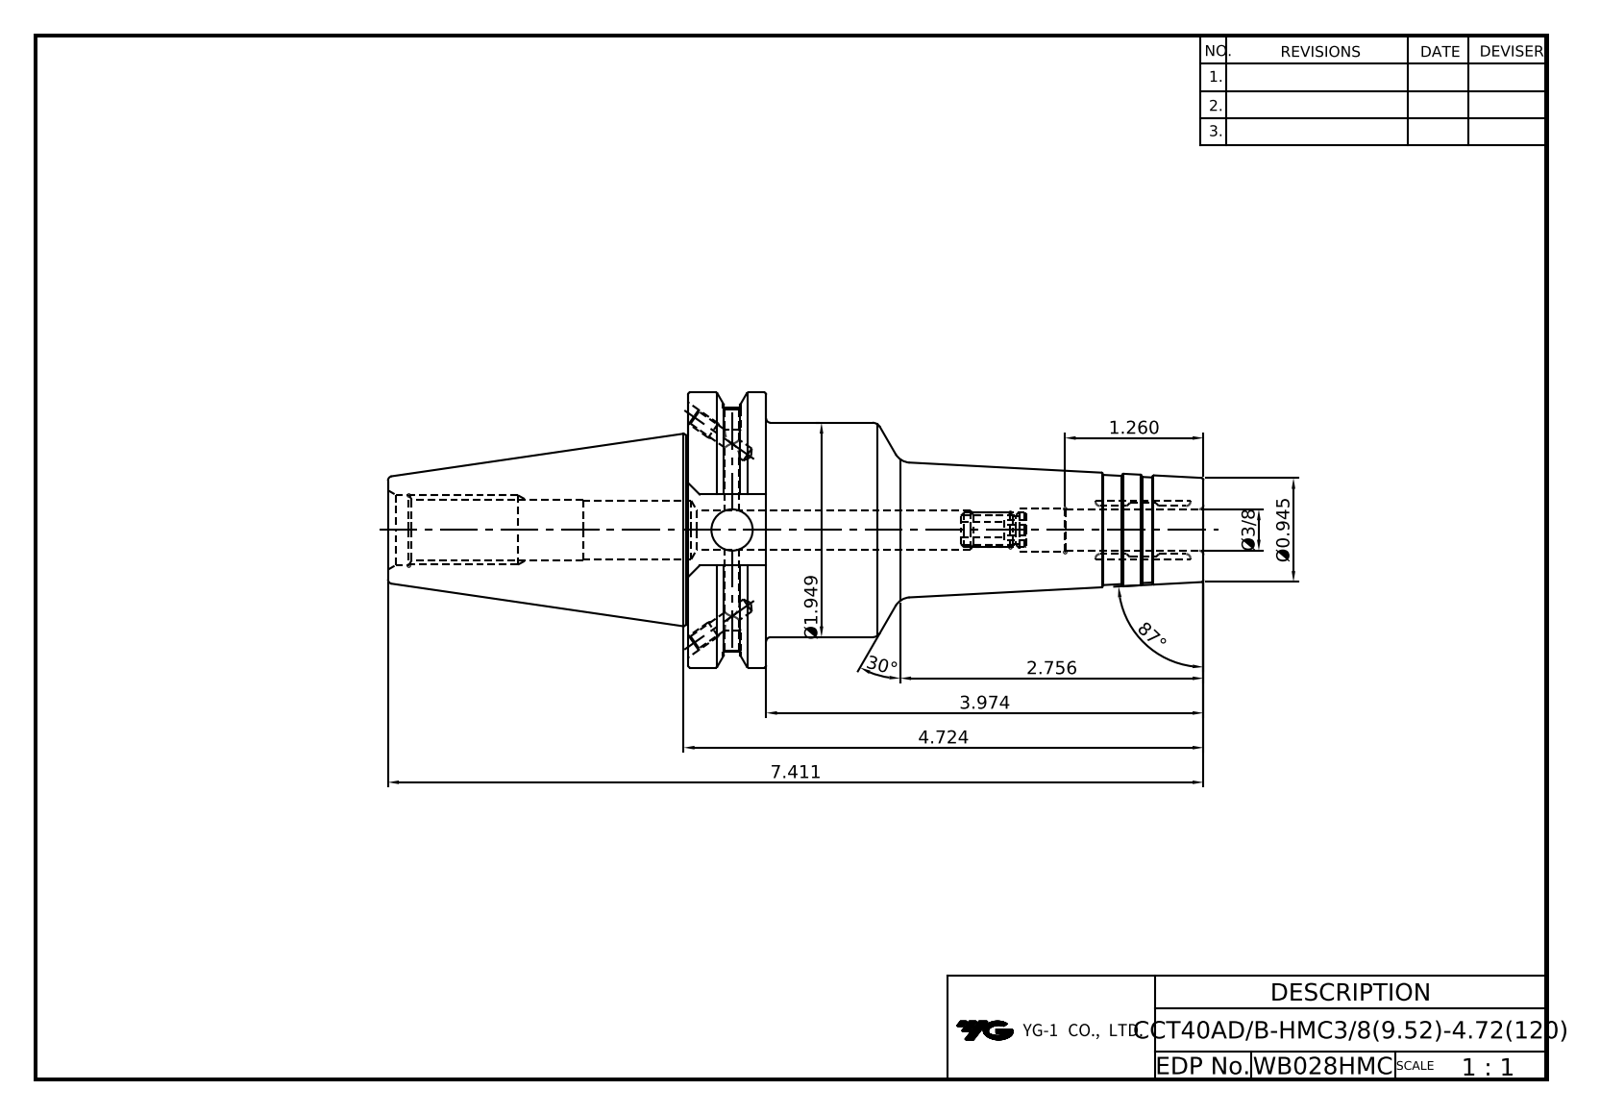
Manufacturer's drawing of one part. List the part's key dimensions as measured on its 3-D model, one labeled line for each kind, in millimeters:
Part name (STEP PRODUCT): LO-CCT40ADB-HMC9.525-120
STEP written by: Autodesk Inventor 2025 (AUTOMOTIVE_DESIGN)
Units: millimetres
Bodies: 1 solid, 107 faces (36 planar, 30 cylindrical, 41 other)
Overall size (bounding box): 188.25 × 63.5 × 61.09
Volume: 197 080 mm³ · Surface area: 33 522 mm²
Round holes (diameter × count): ⌀3.24 ×4, ⌀4 ×2, ⌀4.2 ×2, ⌀9.53 ×2, ⌀6.92 ×1, ⌀9 ×1, ⌀10 ×1, ⌀13 ×1, ⌀13.39 ×1, ⌀16.3 ×1
Round bosses / shafts (diameter × count): ⌀63.5 ×1, ⌀49.5 ×1
Partial cylindrical surfaces — rounded edges, fillets, slot ends (radius × count): R8.19 ×1, R28.15 ×1
Main face-to-face distances: 18.05, 119, 100.95, 47.6, 16.38, 69.25, 87.3, 188.25, 81.3, 12.05
